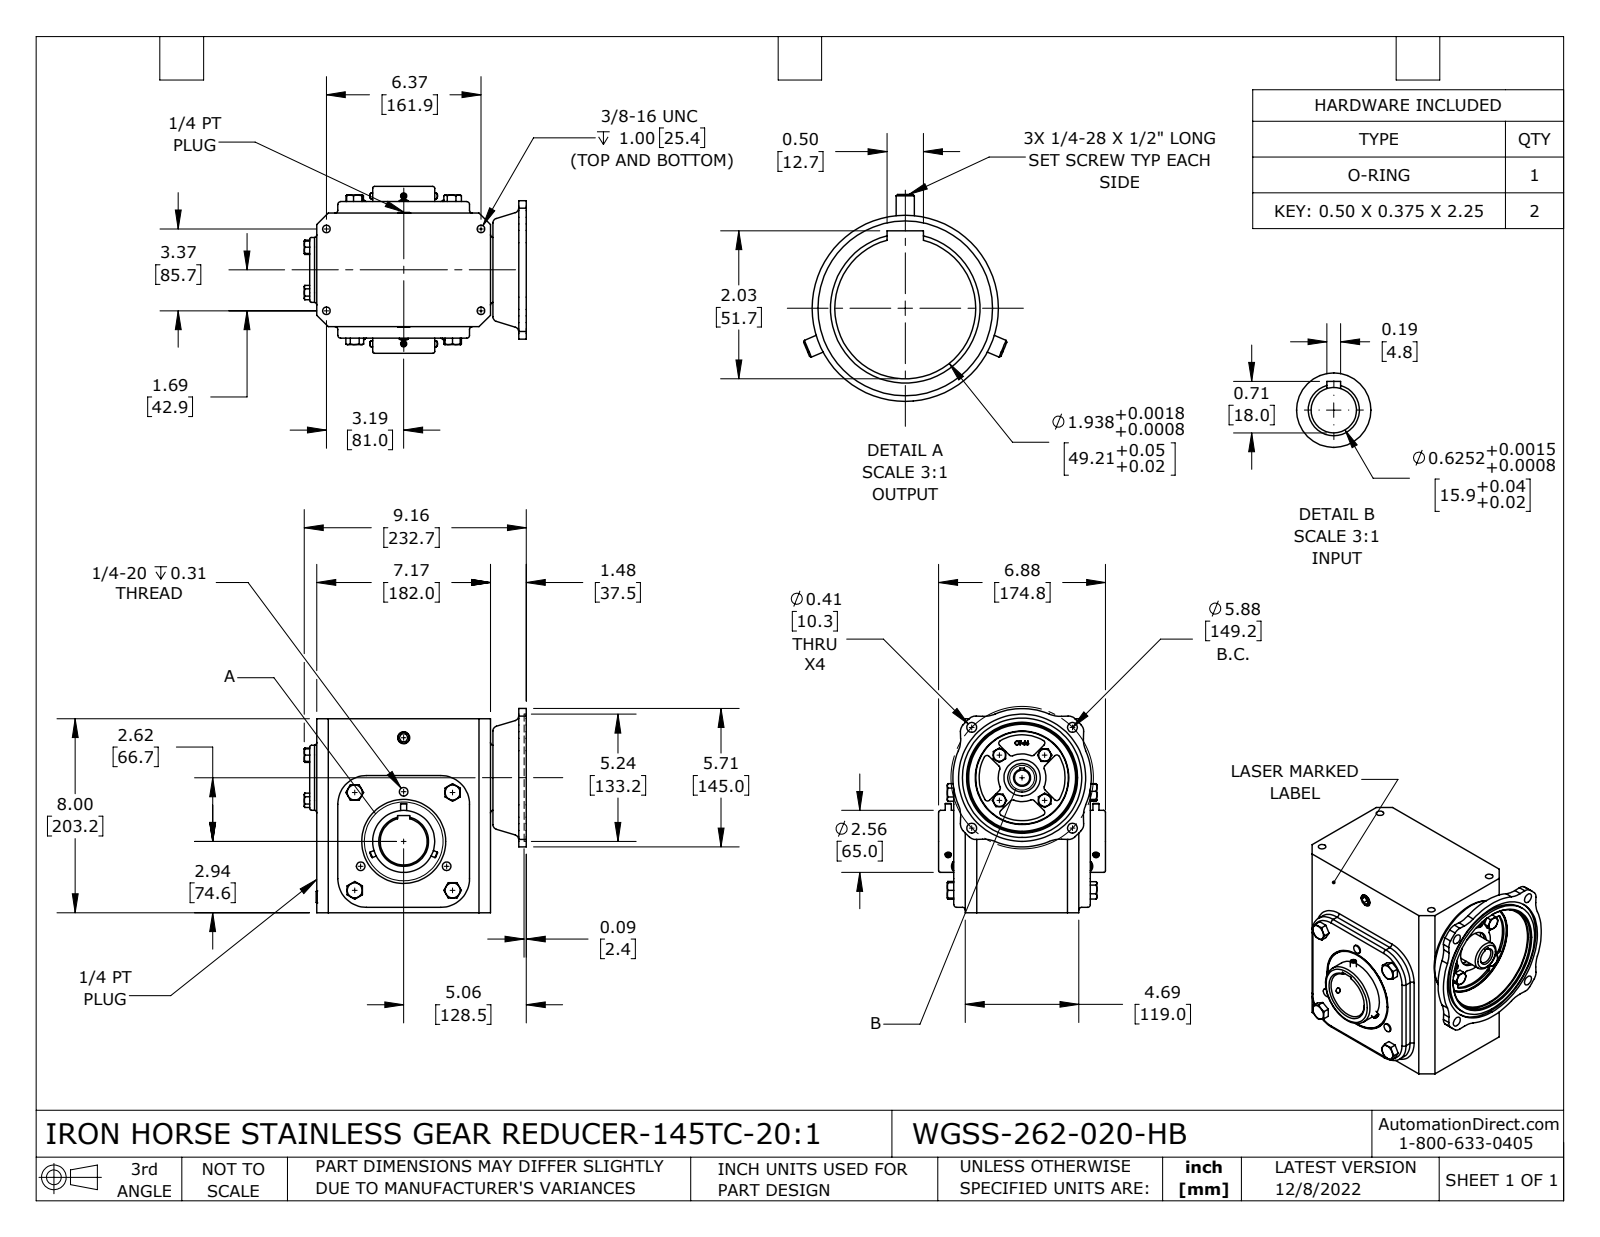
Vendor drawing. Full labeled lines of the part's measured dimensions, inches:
Part name (STEP PRODUCT): WGSS-262-020-HB
STEP written by: SolidWorks 2021 (CONFIG_CONTROL_DESIGN)
Units: inches
Bodies: 7 solids, 669 faces (285 planar, 191 cylindrical, 193 other)
Overall size (bounding box): 9.16 × 8.417 × 6.882
Volume: 289.1 in³ · Surface area: 423.6 in²
Round holes (diameter × count): ⌀0.213 ×6, ⌀0.313 ×4, ⌀0.406 ×4, ⌀0.625 ×1, ⌀0.866 ×1, ⌀1.496 ×1, ⌀1.772 ×1, ⌀1.937 ×1, ⌀2.047 ×1, ⌀3.819 ×1, ⌀4.5 ×1, ⌀5.244 ×1
Round bosses / shafts (diameter × count): ⌀0.25 ×6, ⌀0.354 ×3, ⌀4.921 ×1, ⌀3.465 ×1, ⌀2.559 ×1, ⌀1.181 ×1
Partial cylindrical surfaces — rounded edges, fillets, slot ends (radius × count): R0.118 ×40, R0.394 ×12, R1.181 ×12, R0.079 ×4, R0.984 ×1, R1.772 ×1, R2.854 ×1, R3.27 ×1
Main face-to-face distances: 0.472, 5.157, 8, 7.165, 4.685, 5.63, 7.461, 7.71, 0.295, 1.161
Hole centre spacings: 2.937, 3.465, 4.154, 5.707, 6.094, 3.375, 5.875, 6.375
